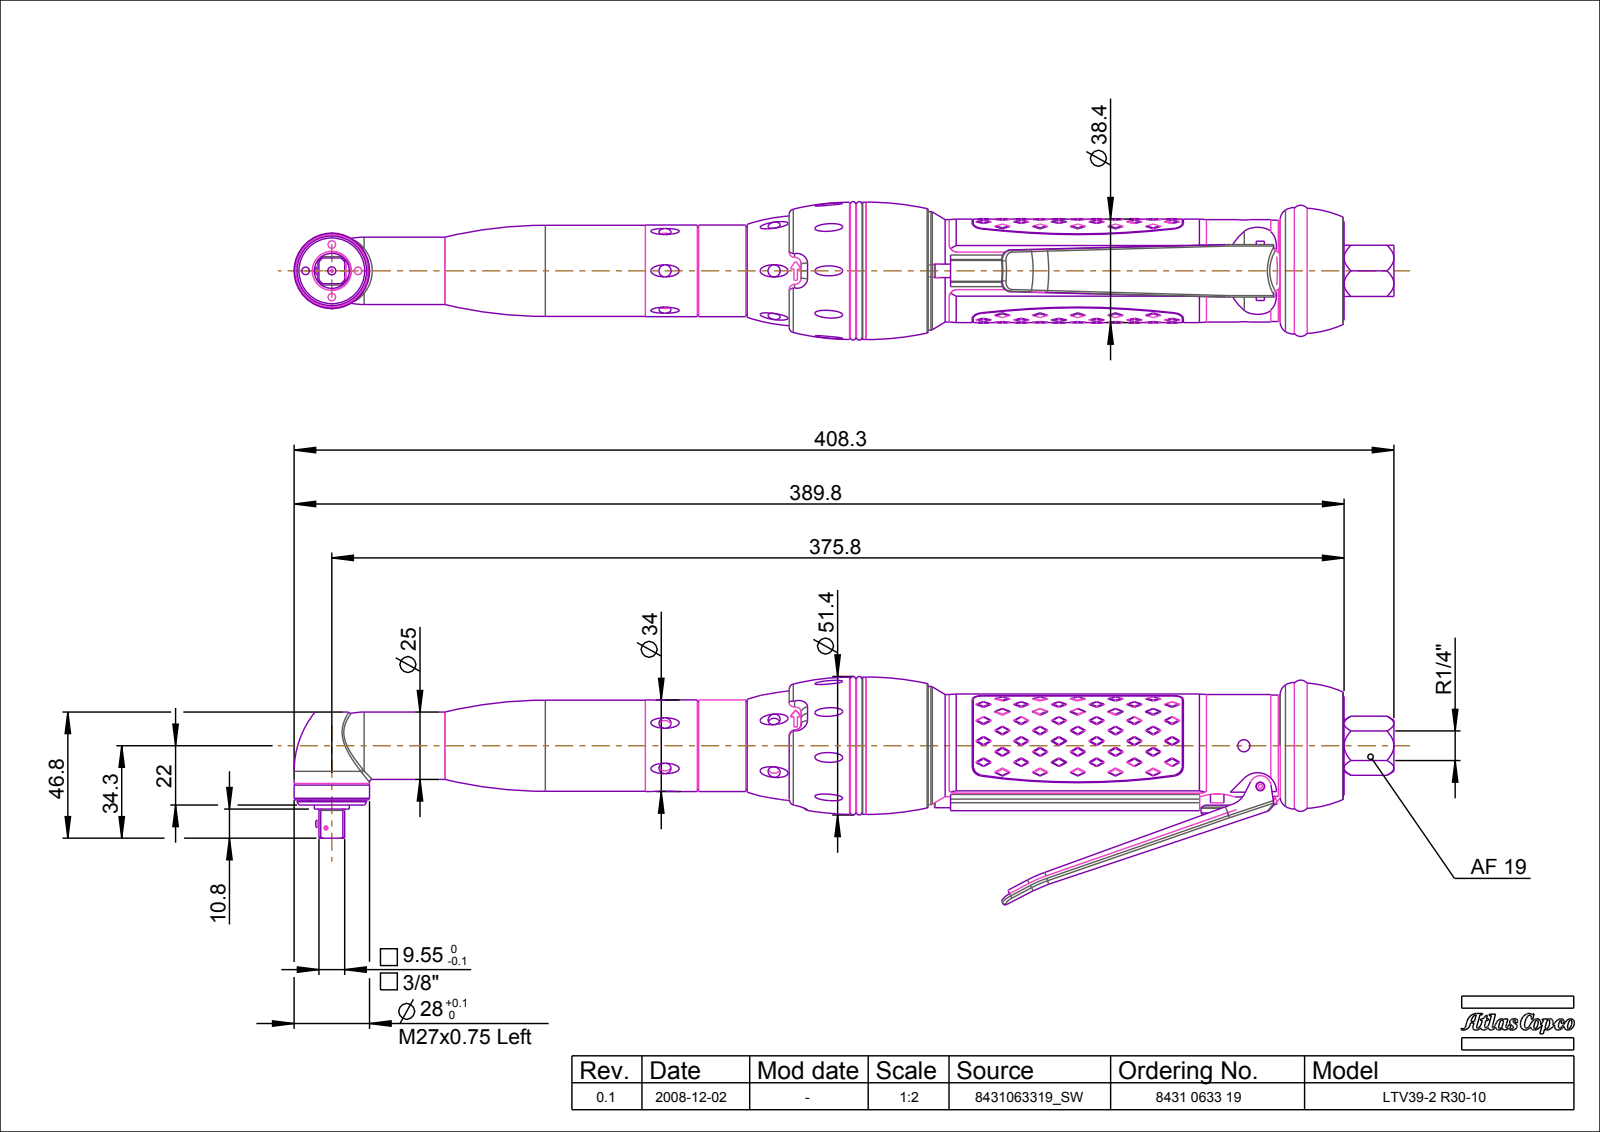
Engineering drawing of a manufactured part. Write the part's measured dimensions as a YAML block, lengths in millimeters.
part_name: "4210437800_AF0; 4210202903_AF0; 4210437100; 4210437180_ASM (+8 more)"
step_written_by: "CREO PARAMETRIC BY PTC INC, 2015380 (CONFIG_CONTROL_DESIGN)"
units: millimeters
bodies: {solids: 23, faces: 2065, planar: 298, cylindrical: 549, other: 1218}
overall_size: [408.3, 84.76, 51.4]
volume: 186324
surface_area: 172393
round_holes:
  - {diameter: 5.5, count: 10}
  - {diameter: 4, count: 7}
  - {diameter: 4.5, count: 7}
  - {diameter: 5, count: 7}
  - {diameter: 2.8, count: 4}
  - {diameter: 1.6, count: 3}
  - {diameter: 1.5, count: 2}
  - {diameter: 11, count: 2}
  - {diameter: 20, count: 2}
  - {diameter: 0.7, count: 1}
  - {diameter: 2, count: 1}
  - {diameter: 3, count: 1}
round_bosses_or_shafts:
  - {diameter: 13, count: 2}
  - {diameter: 12, count: 2}
  - {diameter: 5, count: 2}
  - {diameter: 50.9, count: 1}
  - {diameter: 47.4, count: 1}
  - {diameter: 47, count: 1}
  - {diameter: 45.3, count: 1}
  - {diameter: 41.75, count: 1}
partial_cylinders:
  - {radius: 0.2, count: 23}
  - {radius: 2.15, count: 12}
  - {radius: 1, count: 8}
  - {radius: 3, count: 5}
  - {radius: 4, count: 5}
  - {radius: 0.5, count: 4}
  - {radius: 2.5, count: 4}
  - {radius: 4.5, count: 4}
face_to_face_distances: [19, 1.5, 18, 1, 3, 146.6, 177.4, 159.4, 15.8, 158.4]
hole_center_spacings: [13.5, 25.68, 13.2, 15.87, 8.34, 21.84, 27, 1.43]
